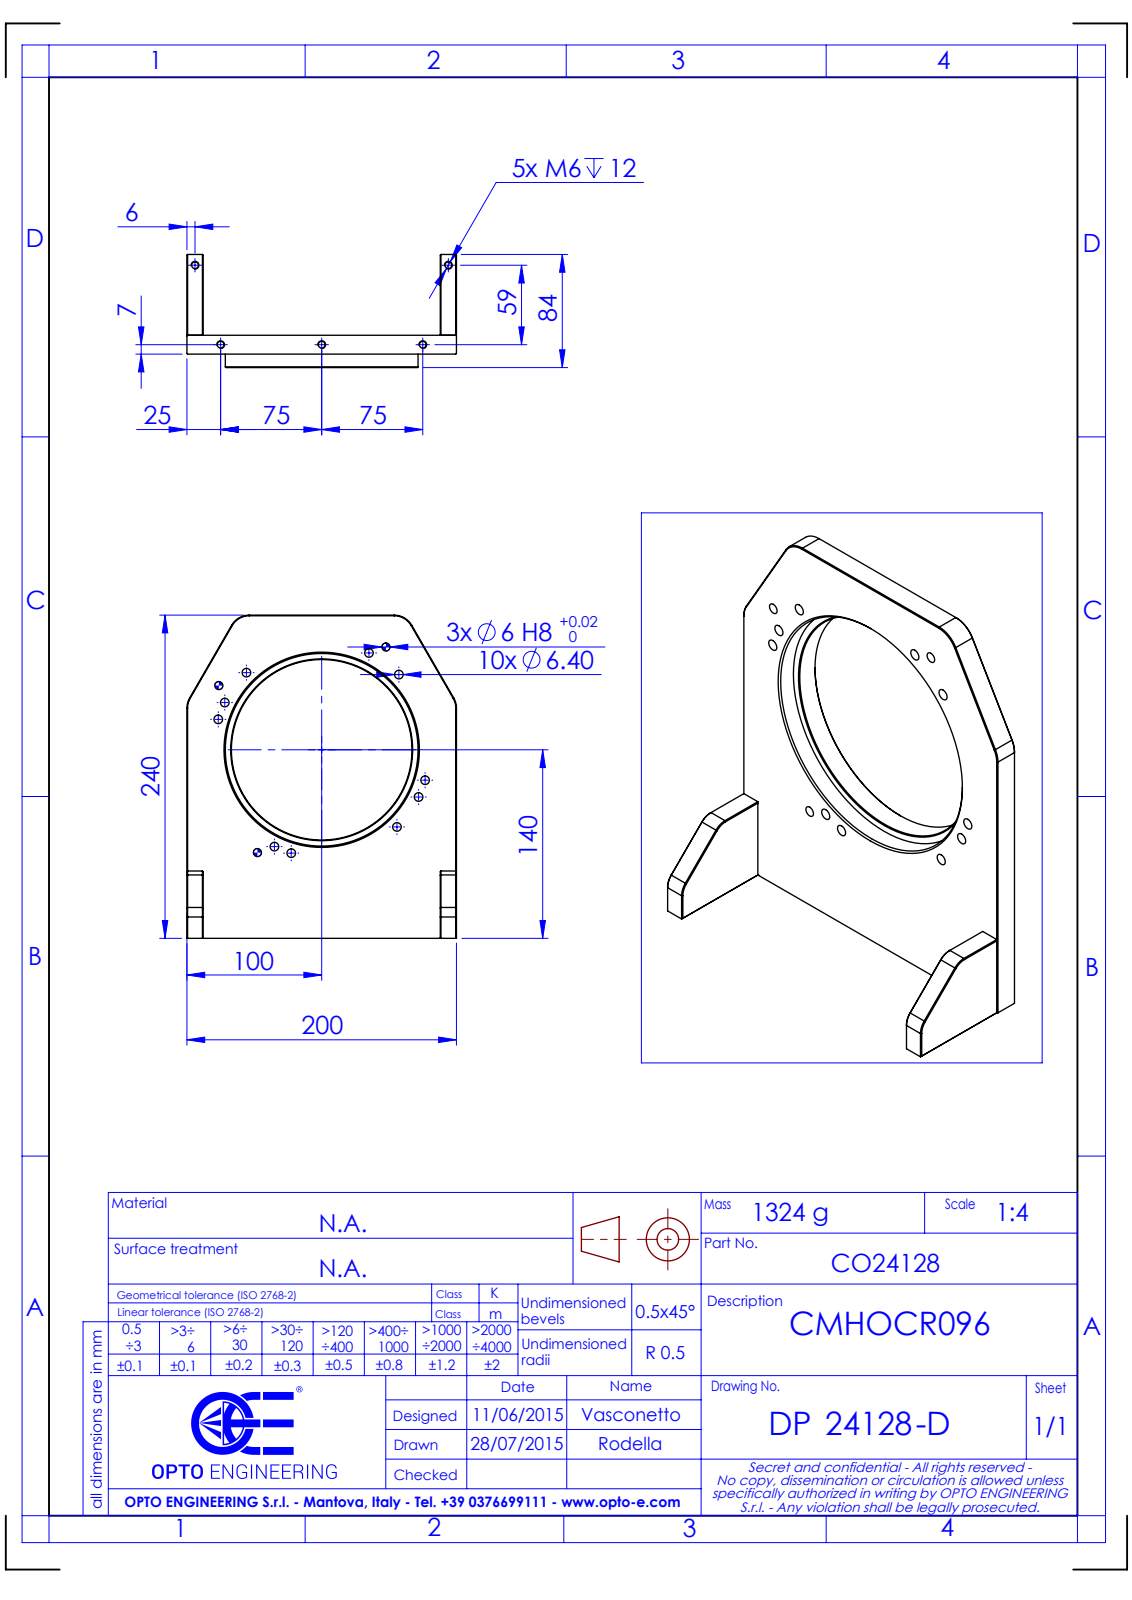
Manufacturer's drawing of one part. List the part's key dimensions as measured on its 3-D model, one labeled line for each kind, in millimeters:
Part name (STEP PRODUCT): DP24128-D_CMHOCR096
STEP written by: SolidWorks 2021 (CONFIG_CONTROL_DESIGN)
Units: millimetres
Bodies: 0 solids, 216 faces (90 planar, 86 cylindrical, 40 other)
Overall size (bounding box): 240 × 200 × 84
Round holes (diameter × count): ⌀11 ×14, ⌀6.4 ×10, ⌀5 ×5, ⌀6 ×3, ⌀134 ×1, ⌀143 ×1
Round bosses / shafts (diameter × count): ⌀10 ×4
Partial cylindrical surfaces — rounded edges, fillets, slot ends (radius × count): R15 ×4, R10 ×2
Main face-to-face distances: 14, 12, 188, 200, 176, 3, 11, 10, 13, 24
Hole centre spacings: 80, 113.13, 13.37, 13.39, 27.4, 89.99, 92.09, 103.27
